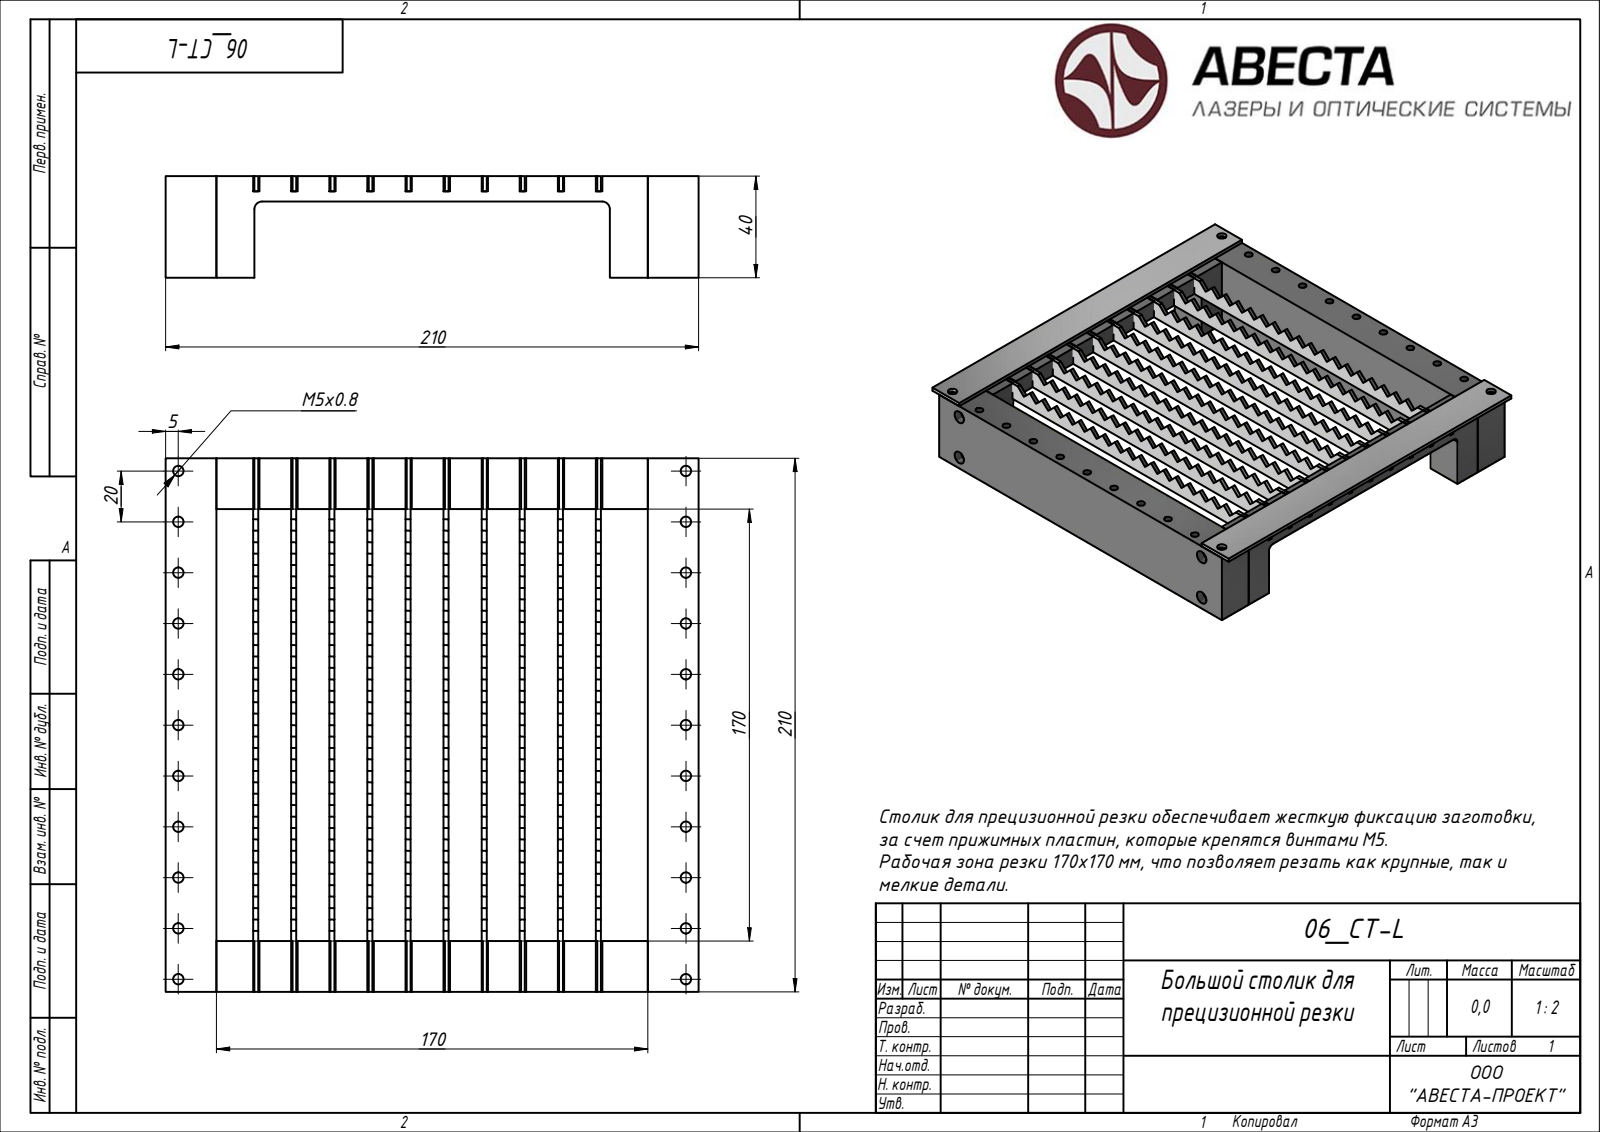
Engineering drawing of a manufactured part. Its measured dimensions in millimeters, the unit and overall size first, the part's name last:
Units: millimetres
Overall size (bounding box): 220 × 210 × 42
Main face-to-face distances: 30, 15, 20, 190, 2, 45, 60, 210, 170, 40
Volume: 477 113 mm³ · Surface area: 153 313 mm²
Bodies: 16 solids, 730 faces (630 planar, 0 cylindrical, 100 other)
Part name (STEP PRODUCT): L01_\X2\041F0440043804360438043C\X0\; L02_\X2\0420043504310440043E\X0\; M02_\X2\042104420435043D043A0430\X0\; M01_Боковина_ЗЕРКАЛО (+1 more)
STEP written by: ST-DEVELOPER v15 (AUTOMOTIVE_DESIGN)
